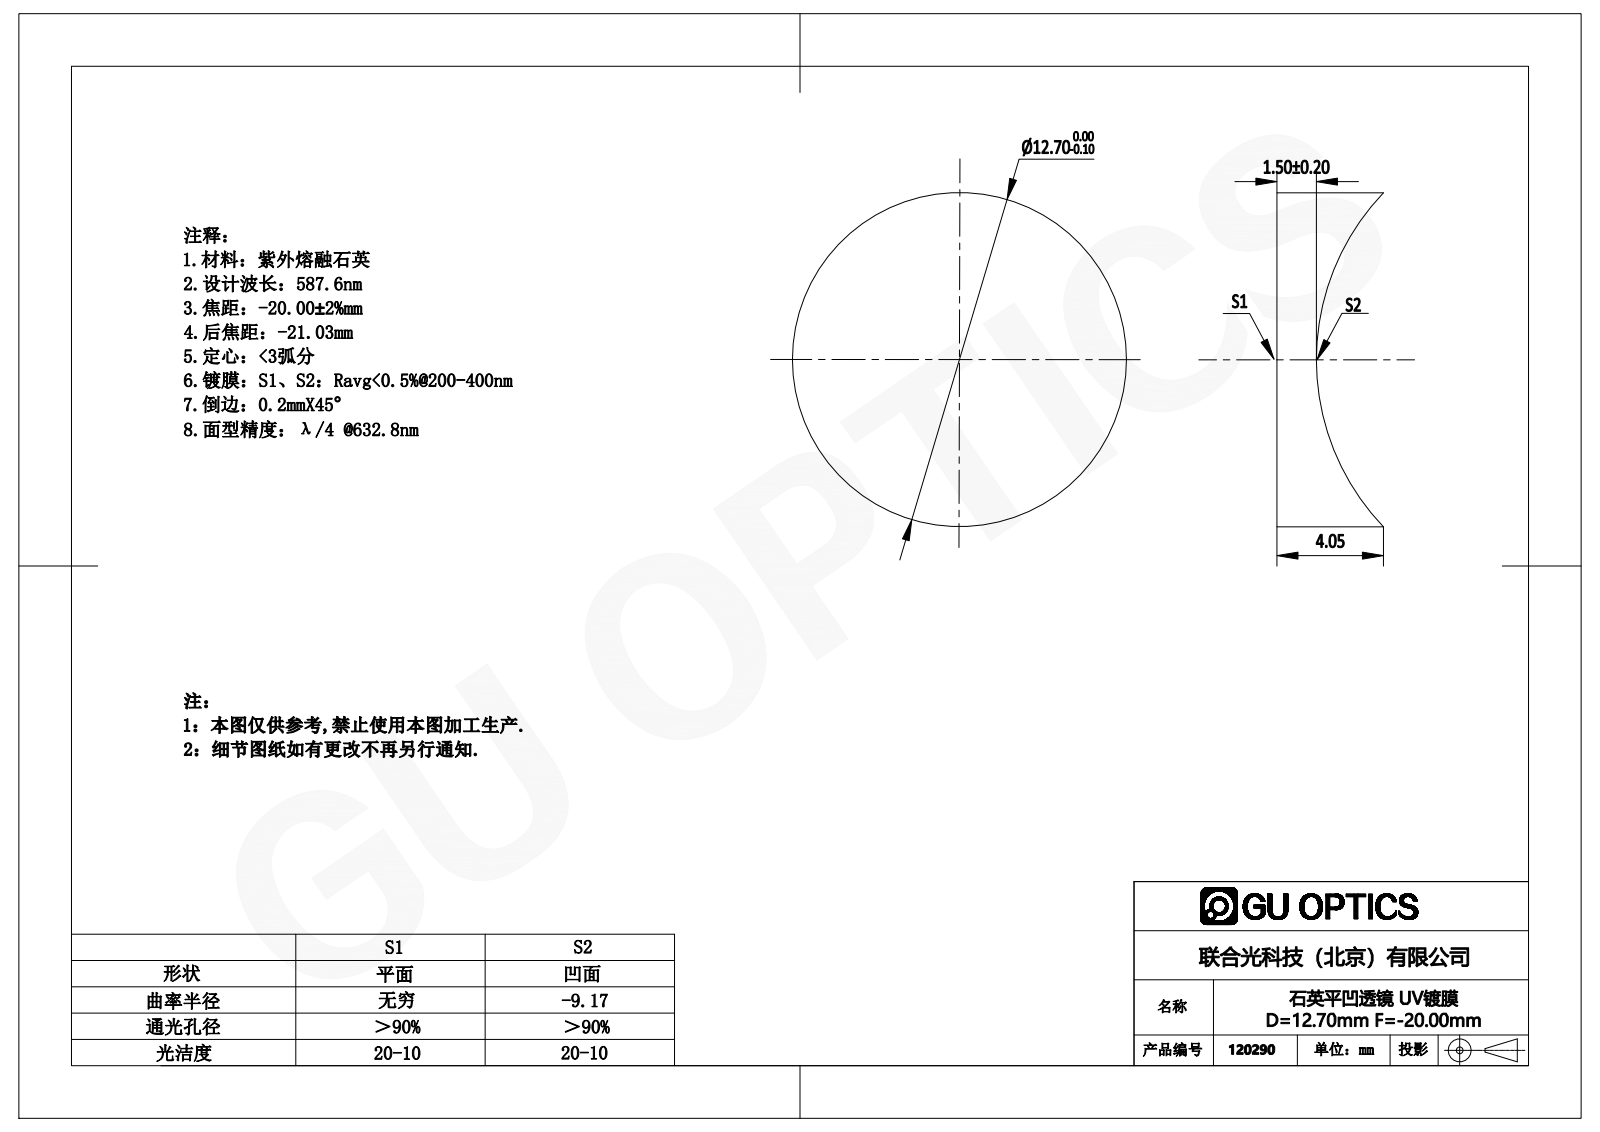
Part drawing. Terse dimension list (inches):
name: 120257
written by: SolidWorks 2016 (AUTOMOTIVE_DESIGN)
unit: in
bodies: 1 solid, 5 faces (1 planar, 2 cylindrical, 2 other)
size: 0.5 × 0.5 × 0.159
volume: 0.021 in³; area: 0.674 in²
bosses: 1× ⌀0.5
